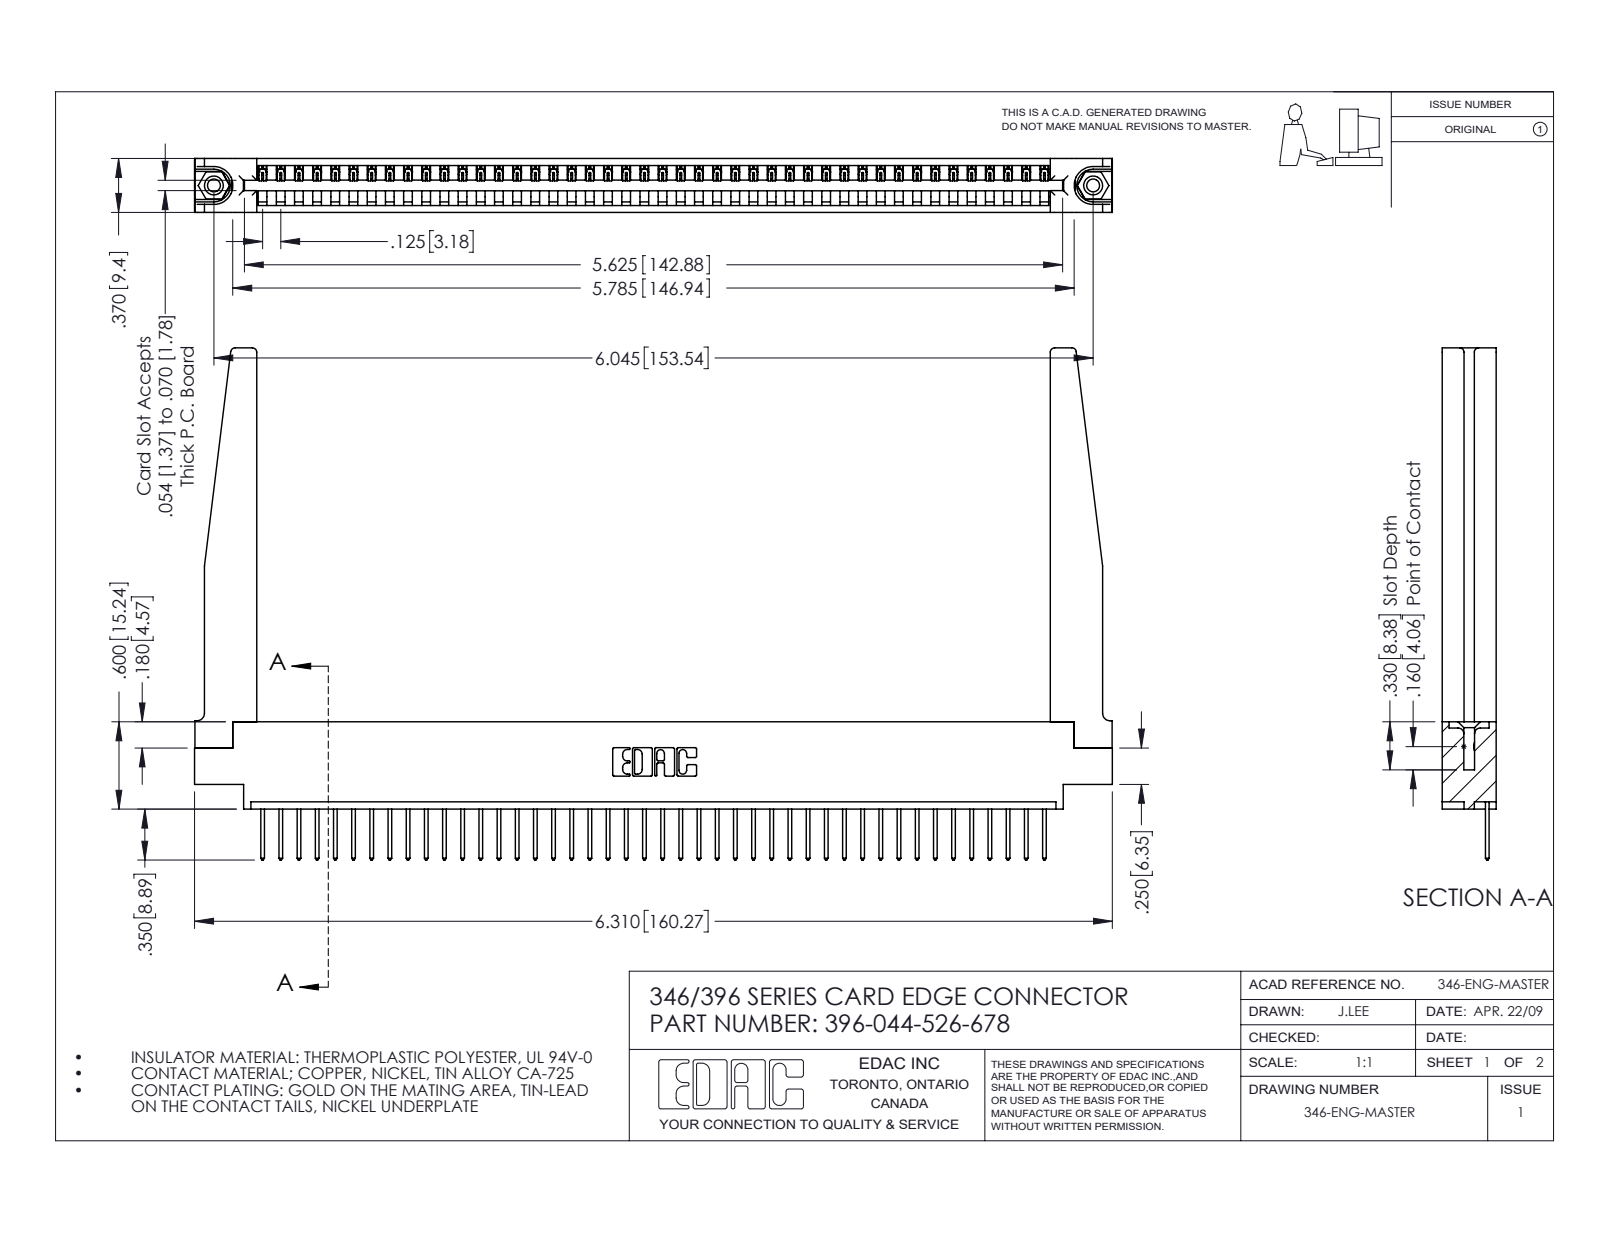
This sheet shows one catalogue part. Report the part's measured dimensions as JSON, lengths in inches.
{"part_name": "345-250-001_345-250-001-102; 346-220-078_345-220-078; 396-044-526-678; 345-292-001_345-293-126 (+1 more)", "step_written_by": "SolidWorks 2016 (CONFIG_CONTROL_DESIGN)", "units": "inches", "bodies": {"solids": 49, "faces": 2912, "planar": 1982, "cylindrical": 878, "other": 52}, "overall_size": [6.31, 3.52, 0.37], "volume_in3": 1.347, "surface_area_in2": 39.73, "round_holes": [[0.089, 2], [0.125, 2], [0.156, 2], [0.064, 1]], "round_bosses_or_shafts": [[0.155, 2]], "partial_cylinders_radius": [[0.006, 88], [0.01, 88], [0.01, 22], [0.03, 8], [0.007, 6], [0.031, 6], [0.026, 3], [0.031, 2]], "face_to_face_distances": [0.37, 0.048, 0.322, 0.072, 0.148, 0.25, 0.15, 0.298, 0.025, 0.222], "hole_center_spacings": [0.246, 5.836, 6.045]}
